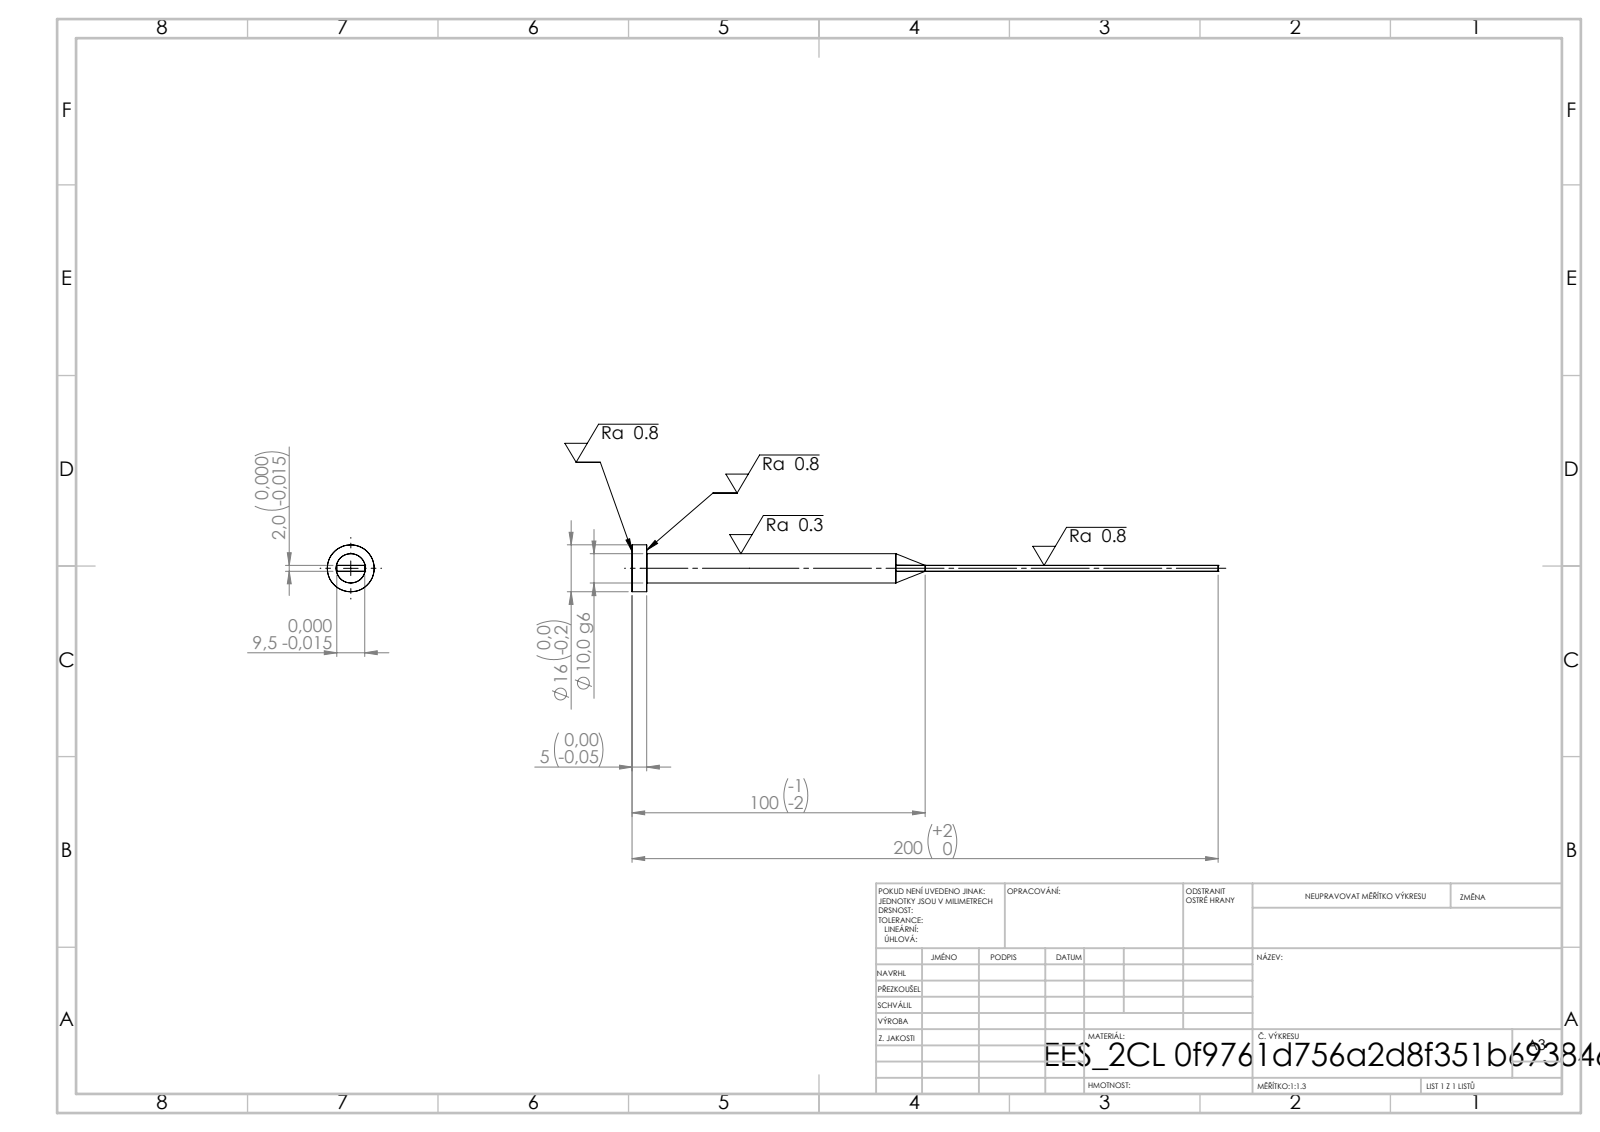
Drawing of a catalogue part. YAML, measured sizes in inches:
step_written_by: "SolidWorks 2019 (CONFIG_CONTROL_DESIGN)"
units: inches
bodies: {solids: 1, faces: 15, planar: 7, cylindrical: 4, other: 4}
overall_size: [7.874, 0.63, 0.63]
volume: 0.613
surface_area: 9.041
round_bosses_or_shafts:
  - {diameter: 0.63, count: 1}
  - {diameter: 0.394, count: 1}
face_to_face_distances: [0.079, 0.374, 0.197, 7.874, 7.677]
